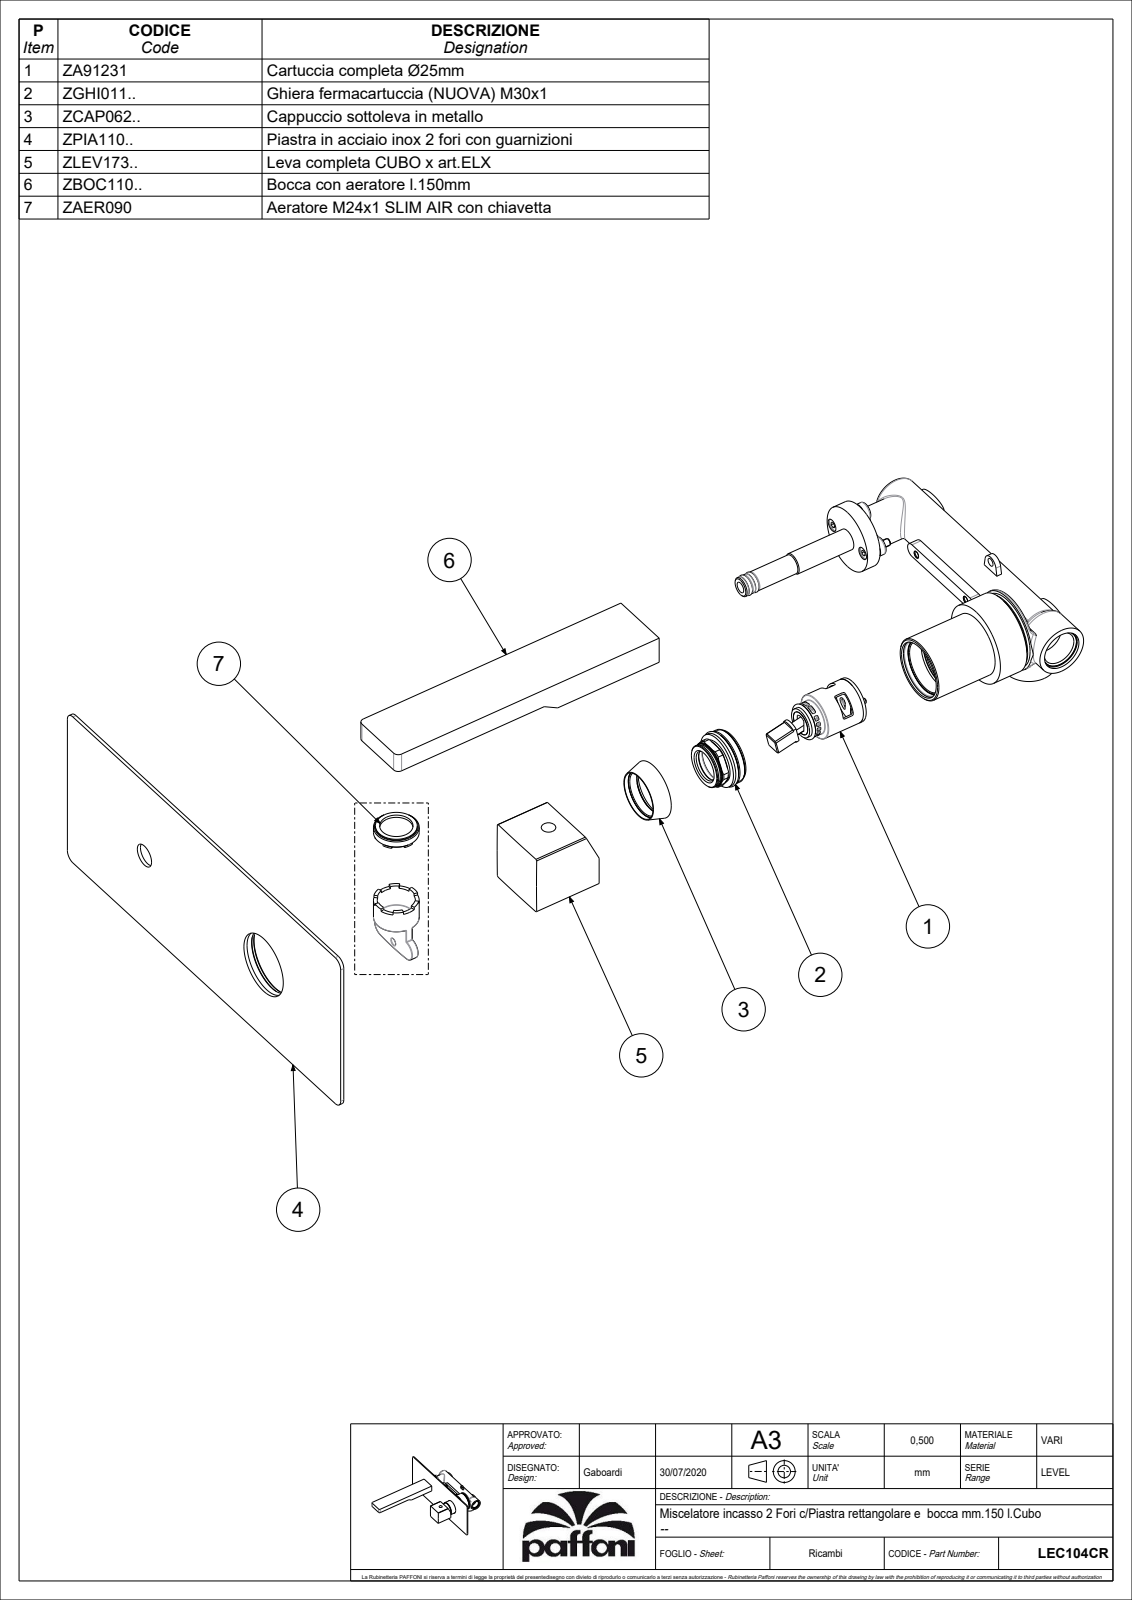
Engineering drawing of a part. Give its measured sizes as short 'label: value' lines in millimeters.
name: LEC104CR
written by: CREO PARAMETRIC BY PTC INC, 2020044 (CONFIG_CONTROL_DESIGN)
unit: mm
bodies: 2 solids, 713 faces (233 planar, 261 cylindrical, 219 other)
size: 250 × 170 × 100
volume: 159 719 mm³; area: 100 170 mm²
holes: 2× ⌀6, 2× ⌀11, 1× ⌀3, 1× ⌀4.2, 1× ⌀5.5, 1× ⌀12, 1× ⌀13, 1× ⌀15, 1× ⌀16.7, 1× ⌀17, 1× ⌀17.5, 1× ⌀19.2
bosses: 1× ⌀35.2, 1× ⌀30, 1× ⌀27.7, 1× ⌀25, 1× ⌀23.8, 1× ⌀22.5, 1× ⌀19, 1× ⌀18.5
rounds: 56× R0.5, 7× R1, 4× R2, 4× R5, 2× R2.1, 2× R2.5, 2× R3, 2× R3.5
face distances: 2, 11.5, 9.75, 26.25, 36, 5, 35, 16.5, 14.75, 73.5
hole spacings: 109, 156.61
